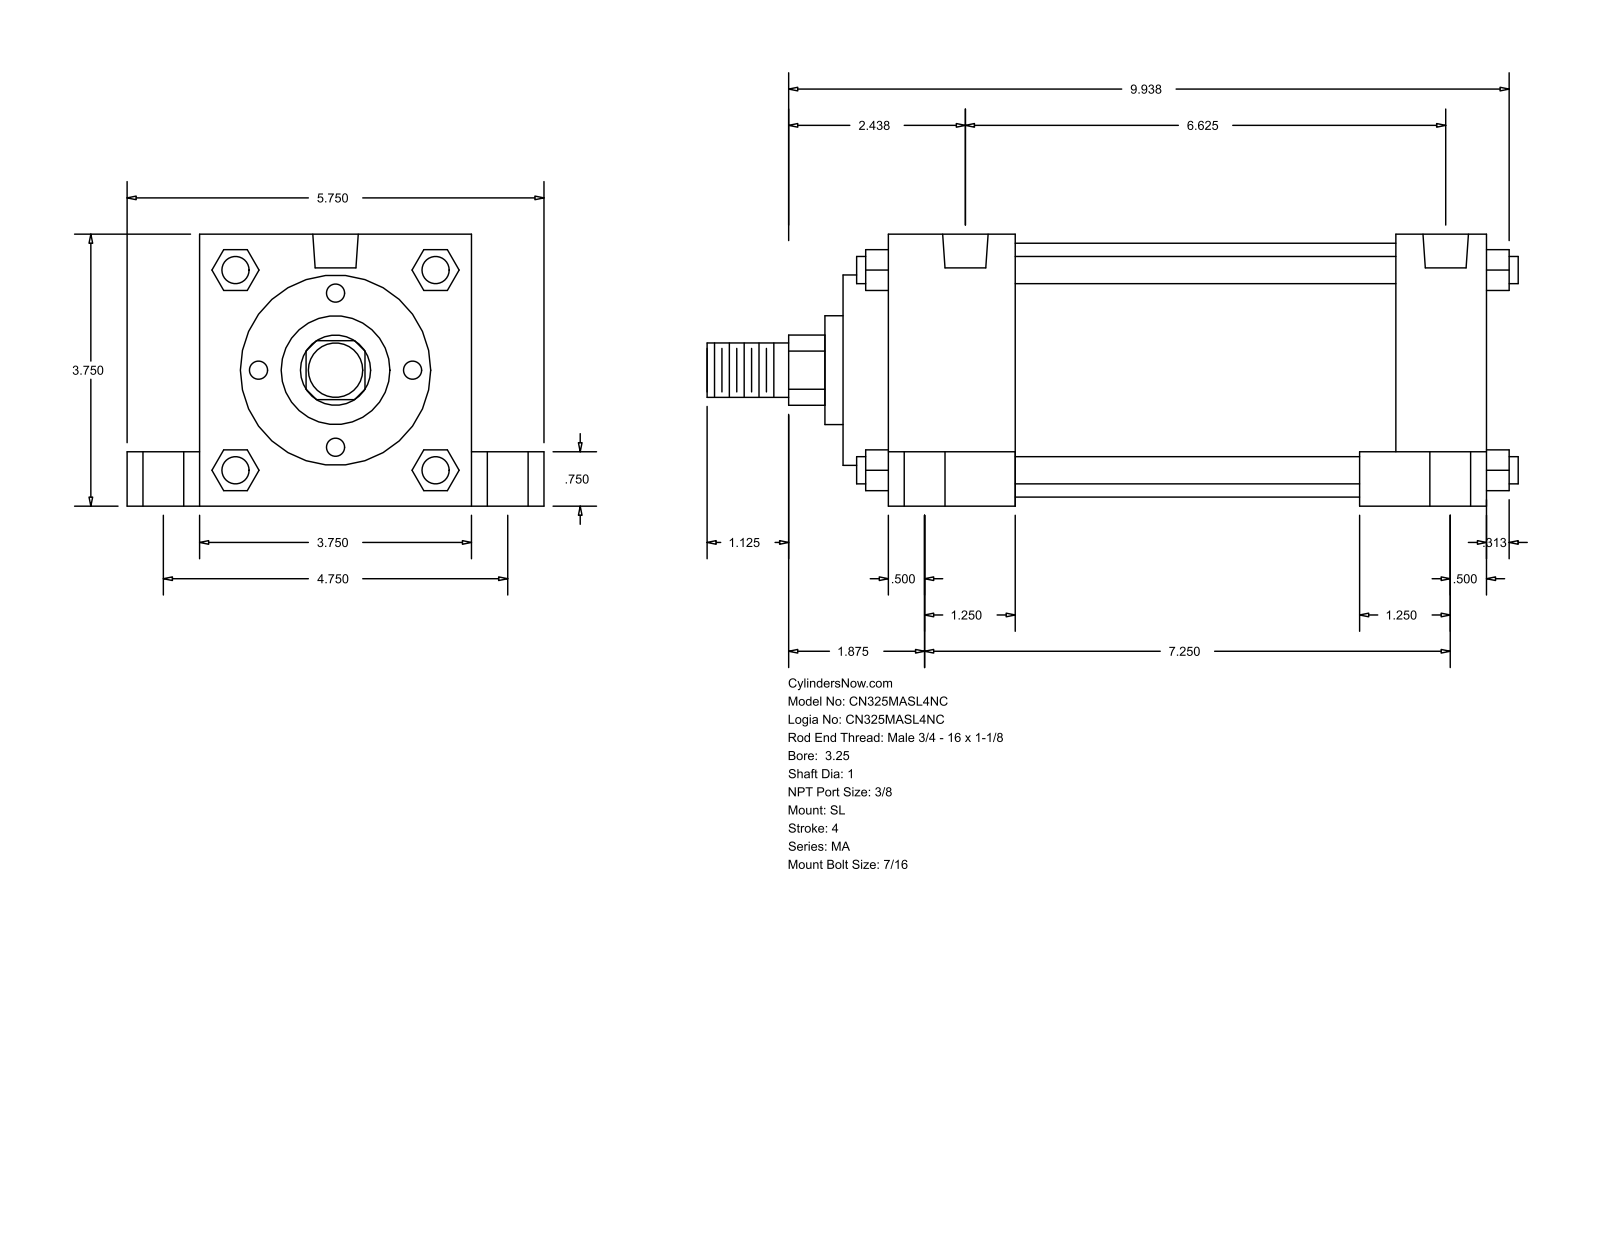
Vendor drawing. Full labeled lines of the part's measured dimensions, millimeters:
Part name (STEP PRODUCT): MA_SL__0325_1
STEP written by: GSSL Pune (CONFIG_CONTROL_DESIGN)
Units: millimetres
Bodies: 0 solids, 150 faces (113 planar, 37 cylindrical, 0 other)
Overall size (bounding box): 284.16 × 146.05 × 95.25
Round holes (diameter × count): ⌀11.11 ×4, ⌀14.29 ×4, ⌀20.64 ×4, ⌀15.93 ×2
Round bosses / shafts (diameter × count): ⌀9.53 ×4, ⌀88.9 ×1, ⌀66.67 ×1, ⌀38.1 ×1, ⌀25.4 ×1, ⌀19.05 ×1
Partial cylindrical surfaces — rounded edges, fillets, slot ends (radius × count): R12.29 ×1
Main face-to-face distances: 95.24, 209.55, 15.87, 25.41, 120.65, 225.42, 19.05, 177.8, 31.75, 44.46
Hole centre spacings: 4.76, 60.35, 60.66, 62, 63.27, 120.66, 158.76, 163.52
